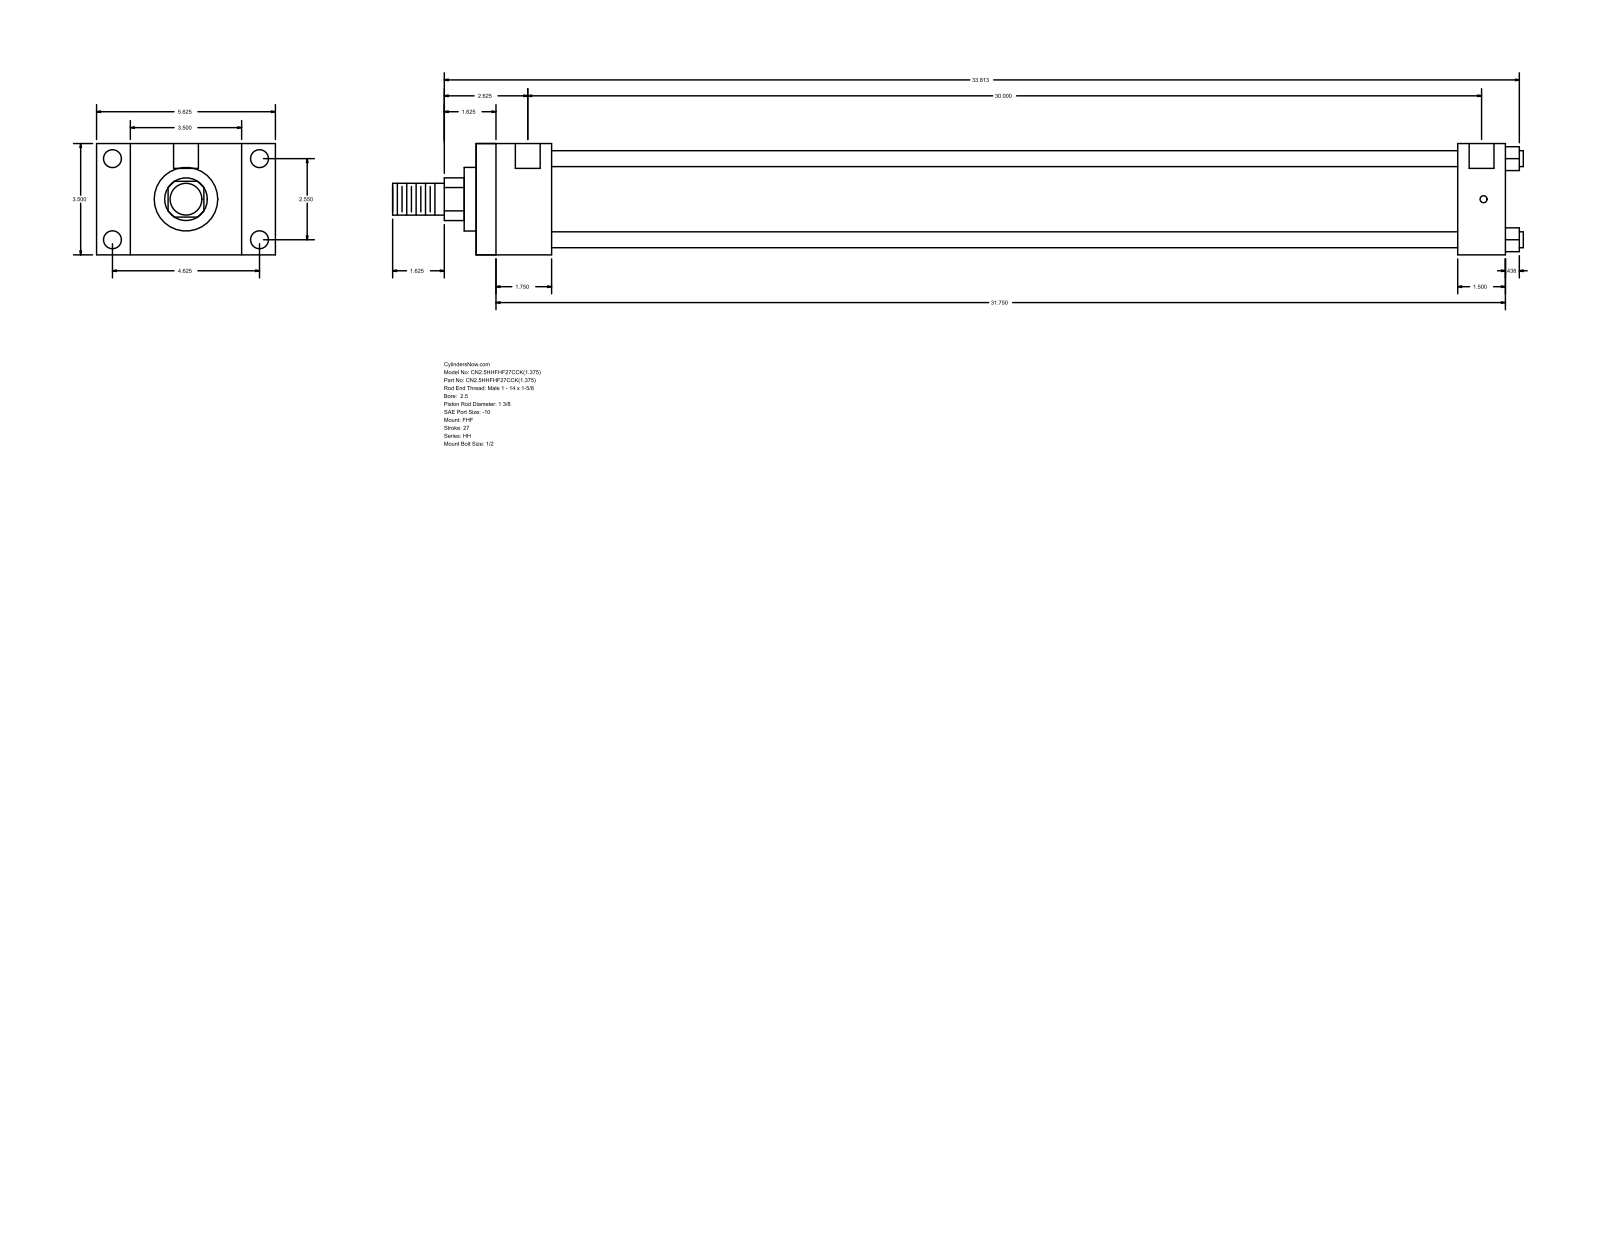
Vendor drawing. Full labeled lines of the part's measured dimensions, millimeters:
Part name (STEP PRODUCT): HH_FHF__0250_1.375
STEP written by: GSSL Pune (CONFIG_CONTROL_DESIGN)
Units: millimetres
Bodies: 0 solids, 88 faces (60 planar, 28 cylindrical, 0 other)
Overall size (bounding box): 903.29 × 142.88 × 88.9
Round holes (diameter × count): ⌀5.56 ×4, ⌀14.3 ×4, ⌀19.84 ×2
Round bosses / shafts (diameter × count): ⌀12.7 ×4, ⌀73.03 ×1, ⌀50.8 ×1, ⌀34.92 ×1, ⌀25.4 ×1
Partial cylindrical surfaces — rounded edges, fillets, slot ends (radius × count): R17.06 ×1
Main face-to-face distances: 88.9, 60.32, 26.99, 115.89, 822.33, 762.01, 142.88, 784.22, 723.9, 38.11
Hole centre spacings: 64.76, 117.48, 134.15, 765.17, 1.58, 1.59, 762, 763.58
